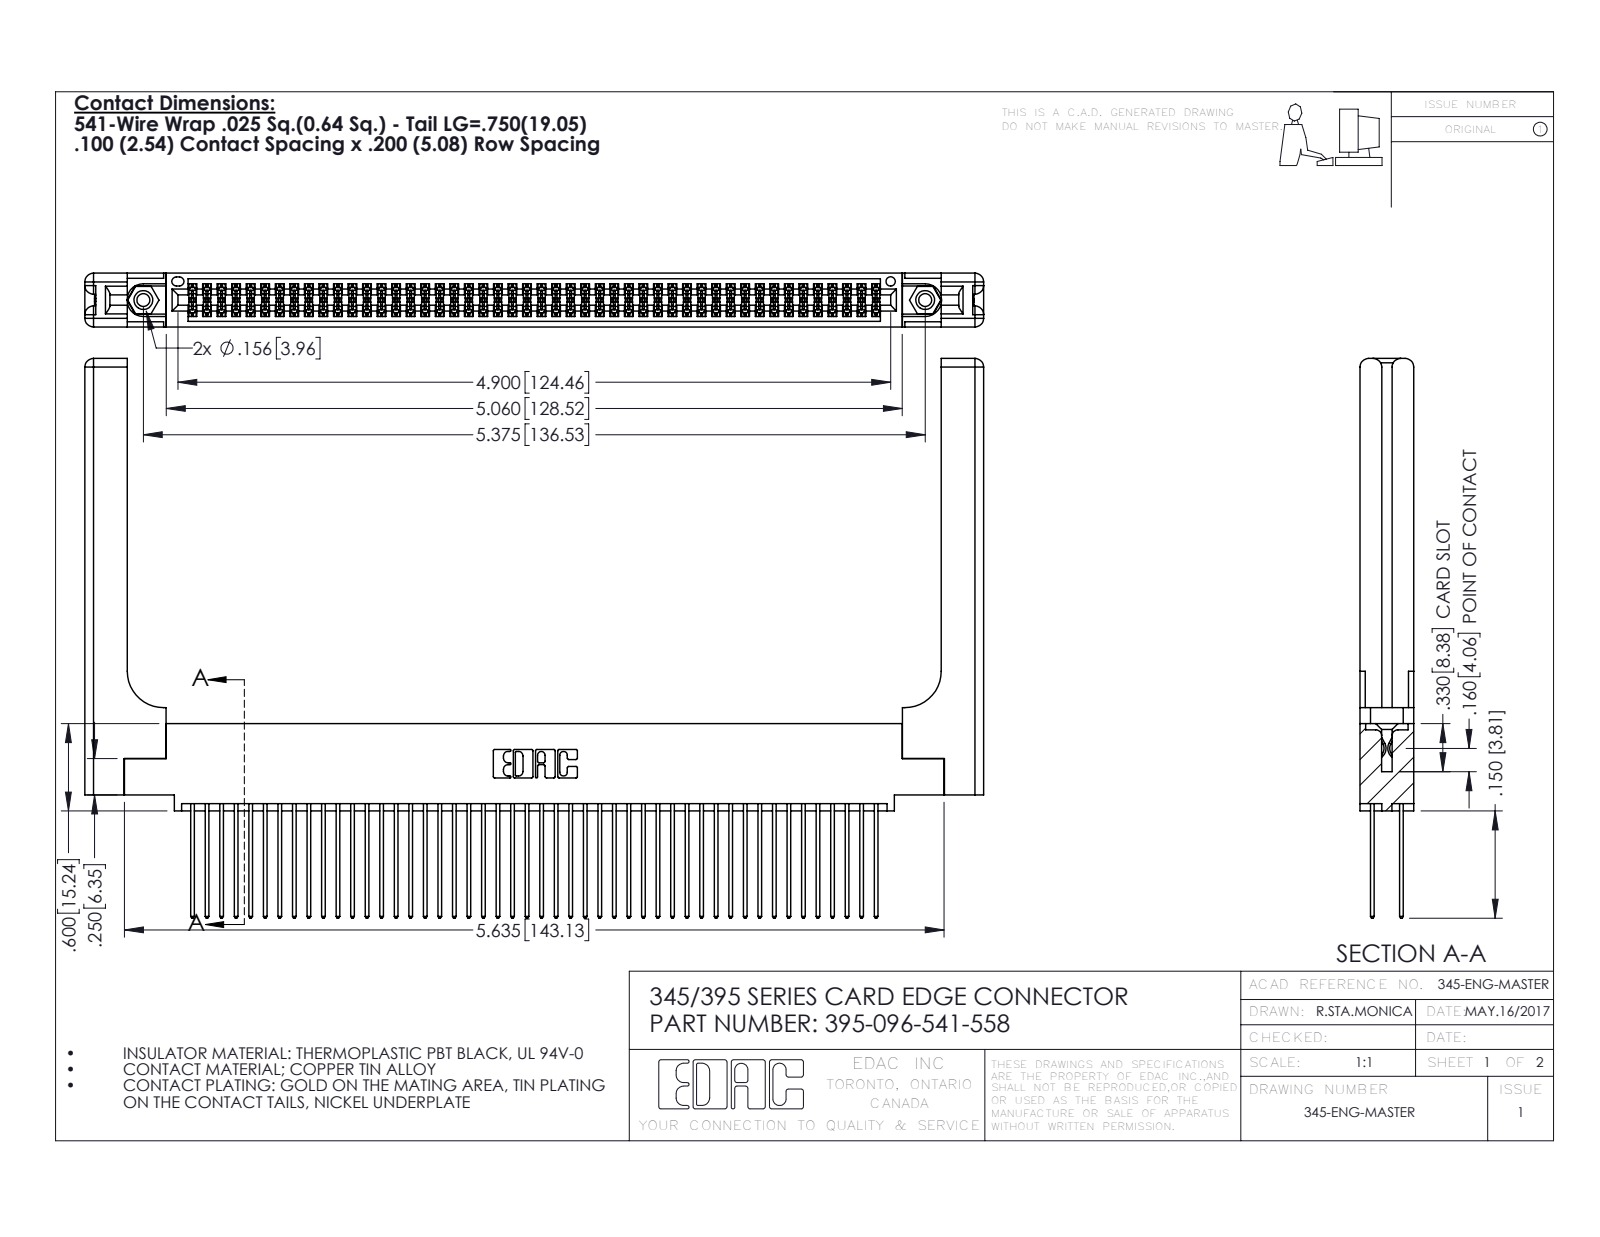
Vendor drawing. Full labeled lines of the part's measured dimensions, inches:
Part name (STEP PRODUCT): 345 Part_0.110 Offset - 0.156 Dia-TH; 345-220-058_345-220-058; 345-292-001_345-293-141; 345-250-001_345-250-001-102 (+1 more)
STEP written by: SolidWorks 2016 (CONFIG_CONTROL_DESIGN)
Units: inches
Bodies: 101 solids, 5186 faces (3400 planar, 1726 cylindrical, 60 other)
Overall size (bounding box): 6.179 × 3.847 × 0.37
Volume: 1.48 in³ · Surface area: 48.33 in²
Round holes (diameter × count): ⌀0.089 ×2, ⌀0.125 ×2, ⌀0.156 ×2, ⌀0.064 ×1
Round bosses / shafts (diameter × count): ⌀0.155 ×2
Partial cylindrical surfaces — rounded edges, fillets, slot ends (radius × count): R0.006 ×144, R0.01 ×96, R0.01 ×22, R0.06 ×16, R0.007 ×6, R0.031 ×6, R0.026 ×3, R0.014 ×2
Main face-to-face distances: 0.072, 0.298, 0.37, 0.098, 0.272, 0.025, 0.2, 0.225, 0.175, 0.148
Hole centre spacings: 0.27, 5.139, 5.375
